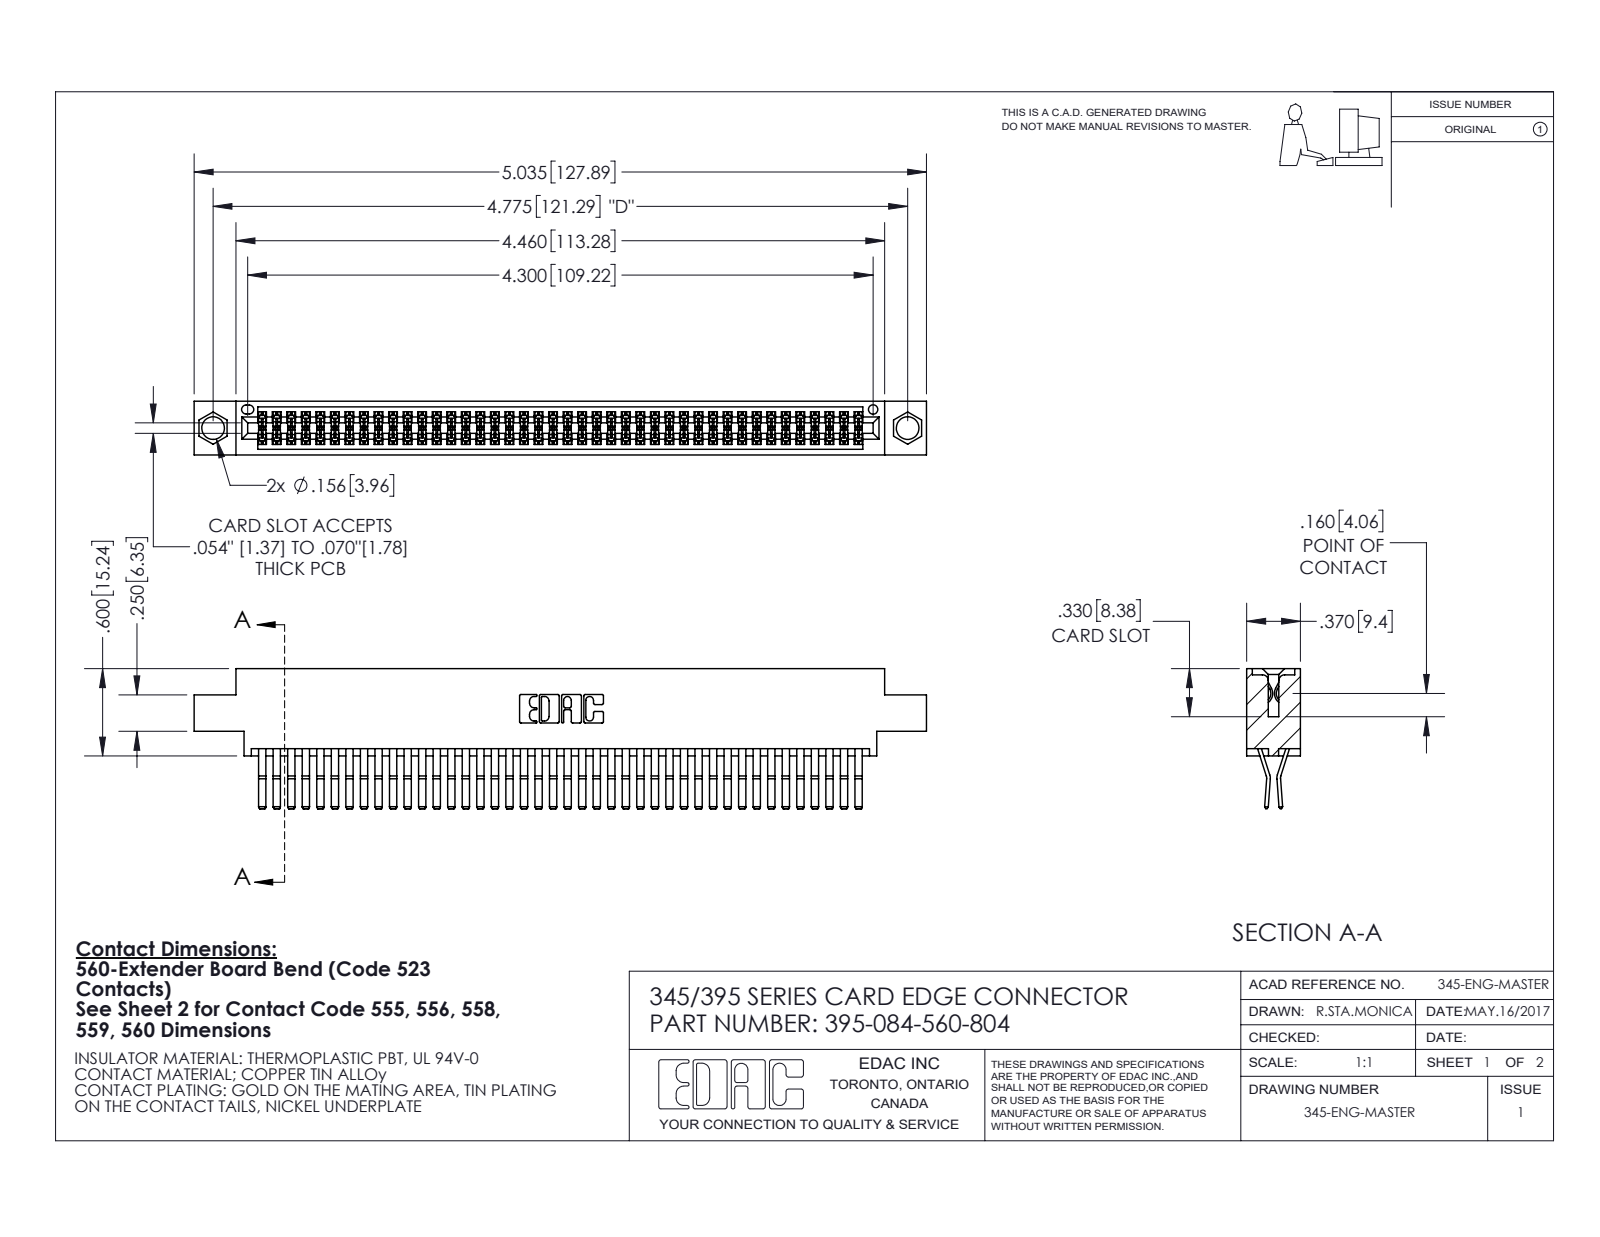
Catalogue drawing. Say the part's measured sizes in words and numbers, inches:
The part is named "345-292-001_560 Tail; 345 Part_0.170 Offset - 0.156 Dia-TI; 395-084-560-804". Its 3-D file was written by "SolidWorks 2020 (CONFIG_CONTROL_DESIGN)". It is 85 solids with 4512 faces: 2870 planar, 1642 cylindrical and 0 other. Overall it measures 5.035 by 0.962 by 0.37 inches. Its volume is 0.778 cubic inches and its surface area 31.41 square inches. Round holes: 2 of diameter 0.156, 1 of diameter 0.064. Partial cylindrical surfaces (rounded edges, fillets, slot ends): 126 of radius 0.006, 22 of radius 0.01, 6 of radius 0.007, 6 of radius 0.031, 3 of radius 0.026, 2 of radius 0.01, 2 of radius 0.014, 2 of radius 0.019. The main face-to-face distances are 0.025, 0.298, 0.072, 0.37, 0.2, 0.098, 0.272, 0.225, 0.175, 0.149. The hole center spacings are 0.27, 4.539, 4.775.
